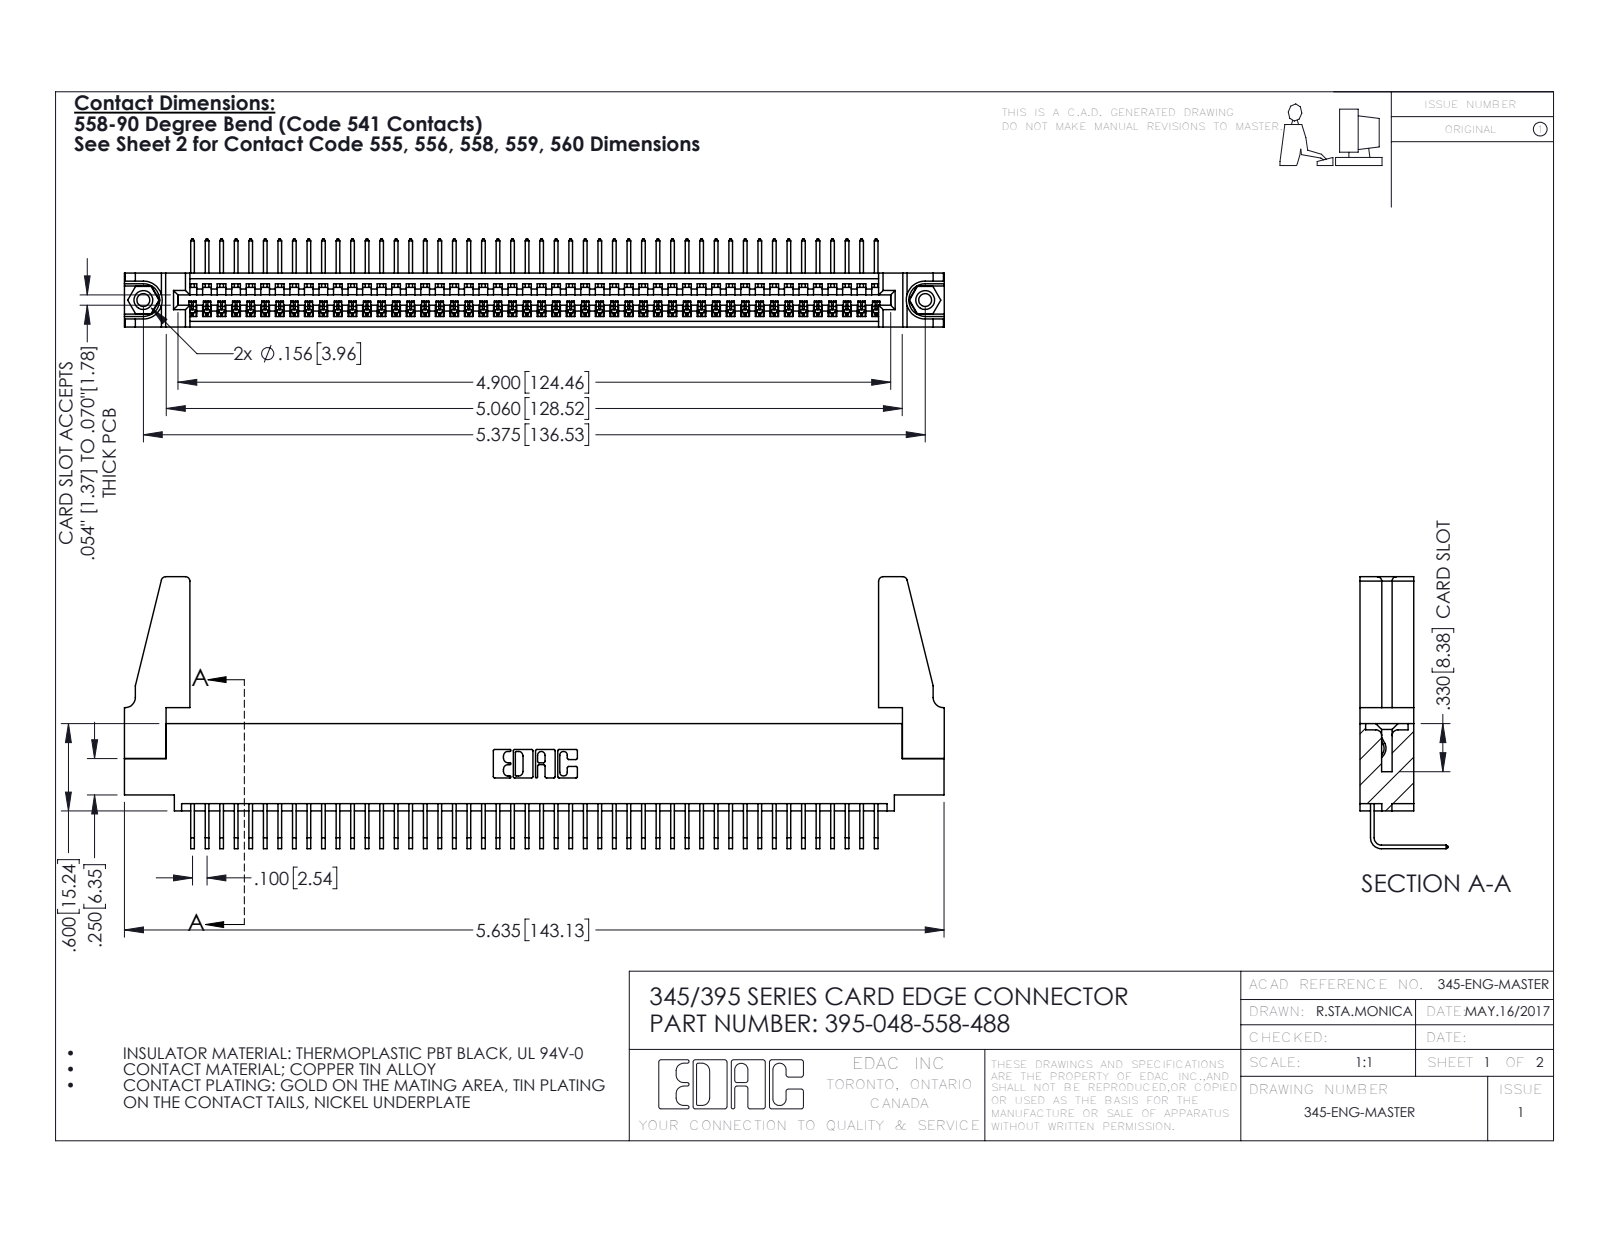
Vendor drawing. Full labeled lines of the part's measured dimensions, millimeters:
Part name (STEP PRODUCT): 345-292-001_558 Tail - 2; 345-220-078_345-220-088; 395-048-558-488; 345-250-001_345-250-001-102 (+1 more)
STEP written by: SolidWorks 2016 (CONFIG_CONTROL_DESIGN)
Units: millimetres
Bodies: 53 solids, 3134 faces (2172 planar, 946 cylindrical, 16 other)
Overall size (bounding box): 143.2 × 47.5 × 15.4
Volume: 16 980 mm³ · Surface area: 22 480 mm²
Round holes (diameter × count): ⌀2.3 ×2, ⌀3.2 ×2, ⌀4 ×2, ⌀1.6 ×1
Round bosses / shafts (diameter × count): ⌀3.9 ×2
Partial cylindrical surfaces — rounded edges, fillets, slot ends (radius × count): R0.2 ×96, R0.3 ×22, R0.8 ×8, R0.2 ×6, R0.8 ×6, R0.7 ×3, R0.8 ×2, R1 ×2
Main face-to-face distances: 1.8, 7.6, 9.4, 5.1, 2.5, 6.9, 0.6, 5.7, 3.8, 1.8
Hole centre spacings: 6.9, 130.5, 136.5
